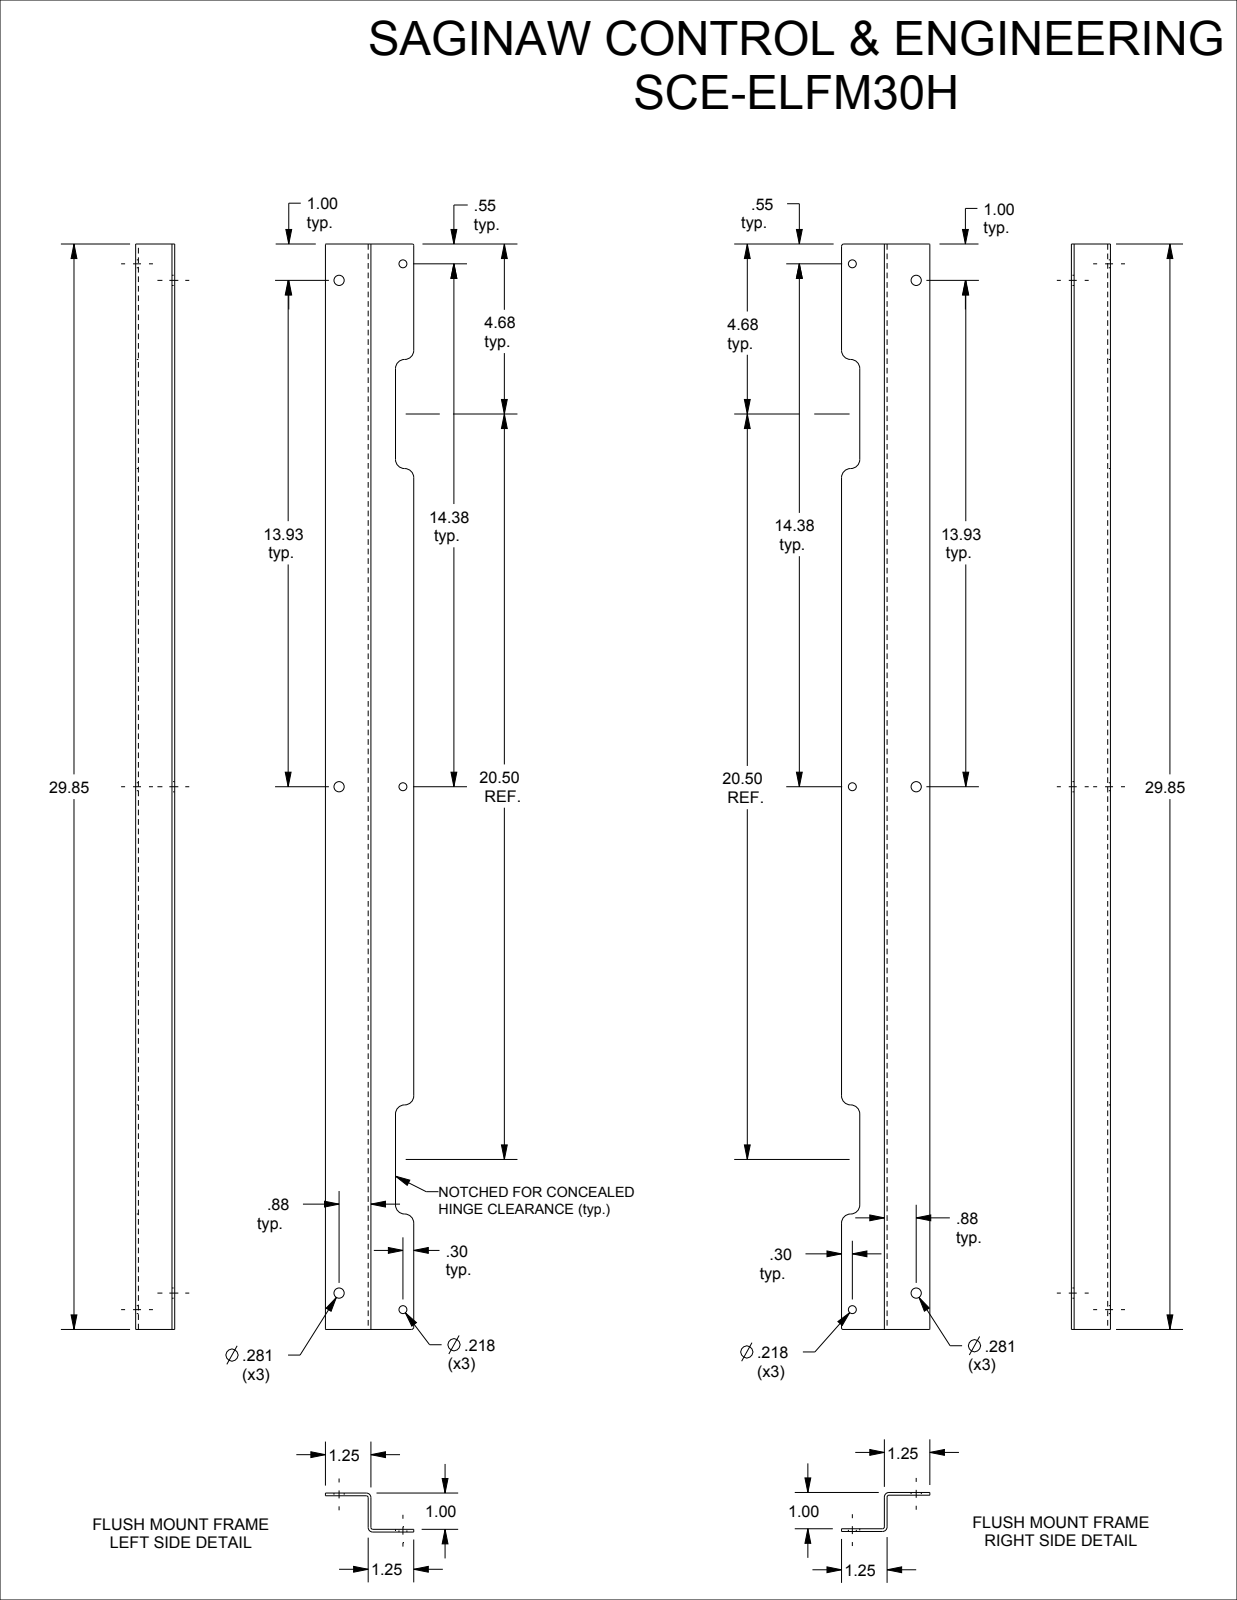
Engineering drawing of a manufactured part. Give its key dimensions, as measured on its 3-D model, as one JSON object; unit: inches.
{"part_name": "SCE-ELFM30H", "step_written_by": "SolidWorks 2019 (CONFIG_CONTROL_DESIGN)", "units": "inches", "bodies": {"solids": 2, "faces": 80, "planar": 36, "cylindrical": 44, "other": 0}, "overall_size": [29.85, 27, 1.073], "volume_in3": 14.5, "surface_area_in2": 397.5, "round_holes": [[0.218, 6], [0.281, 6]], "partial_cylinders_radius": [[0.25, 16], [0.015, 4], [0.051, 4], [0.126, 4], [0.04, 2], [0.063, 2]], "face_to_face_distances": [0.075, 0.075, 0.923, 0.998, 0.998, 1.073, 24.575, 24.65, 24.5, 24.575], "hole_center_spacings": [1.813, 13.925, 14.035, 14.38, 14.487, 24.499, 26.905, 28.176]}
